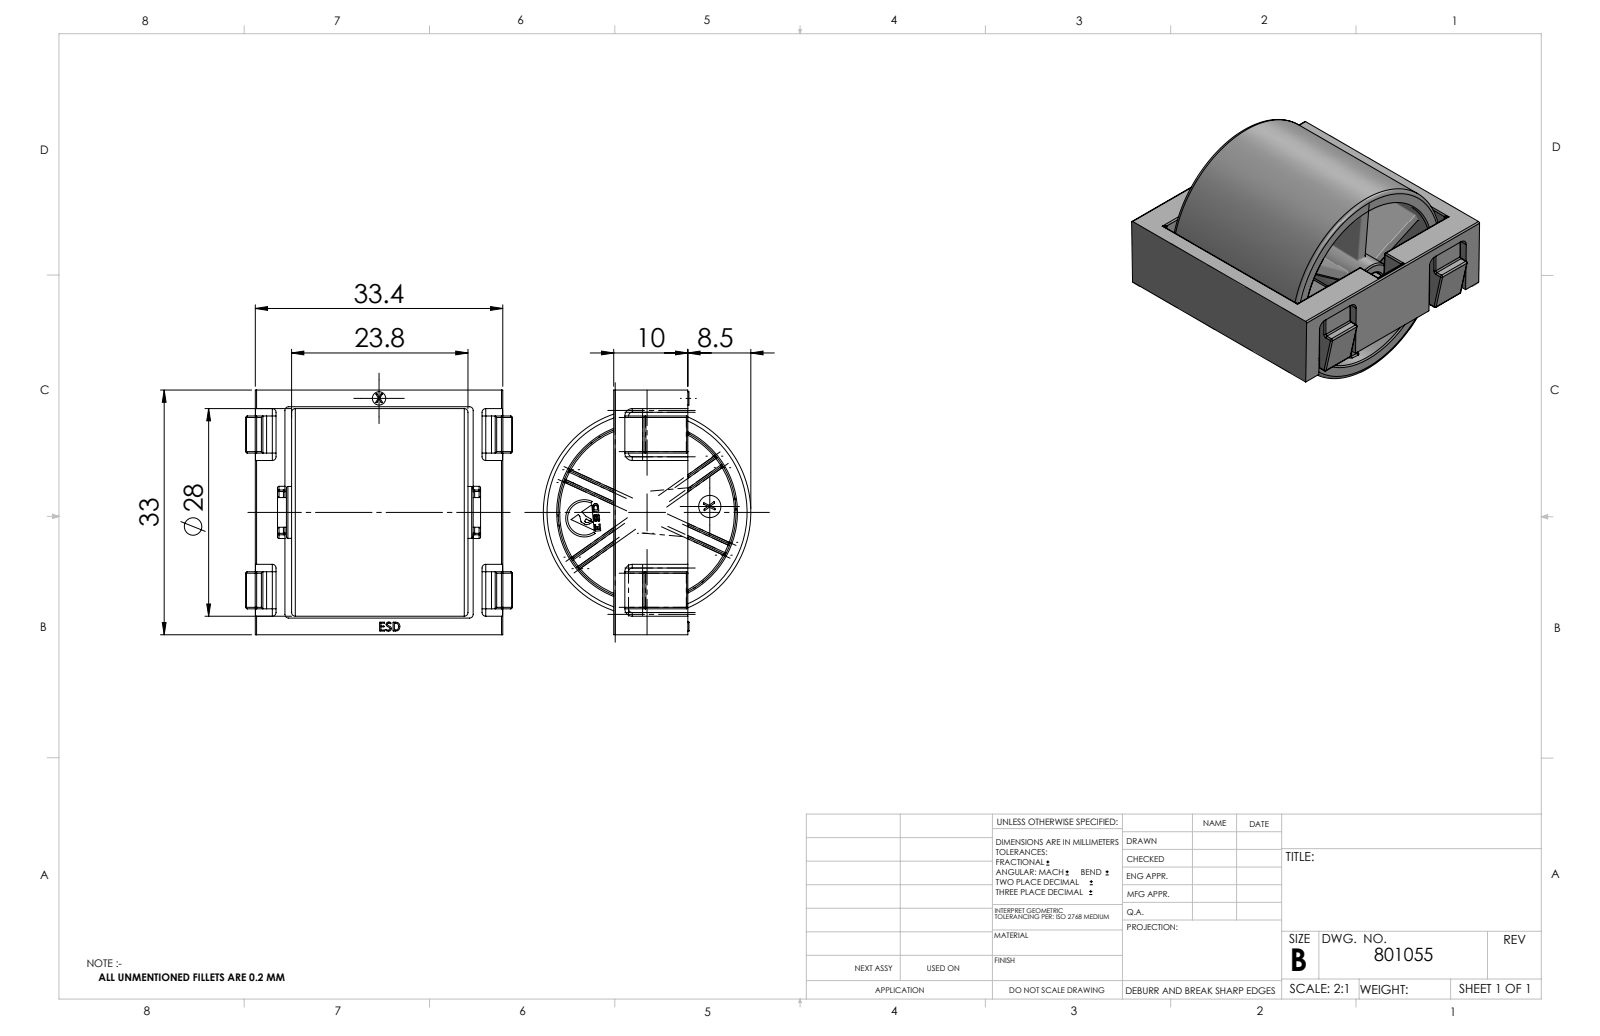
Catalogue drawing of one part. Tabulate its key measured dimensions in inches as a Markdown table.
| quantity | value |
| --- | --- |
| part name | 801055_c_1 |
| STEP written by | SolidWorks 2014 (CONFIG_CONTROL_DESIGN) |
| units | inches |
| bodies | 3 solids, 808 faces (263 planar, 259 cylindrical, 286 other) |
| overall size | 1.413 × 1.299 × 1.102 |
| volume | 0.602 in³ |
| surface area | 18.09 in² |
| round holes (diameter × count) | 0.165 × 1, 0.945 × 1 |
| round bosses / shafts (diameter × count) | 1.102 × 1, 0.276 × 1, 0.157 × 1, 0.118 × 1, 0.071 × 1 |
| partial cylindrical surfaces (radius × count) | 0.008 × 152, 0.02 × 16, 0.039 × 4, 0.081 × 1, 0.089 × 1, 0.099 × 1 |
| main face-to-face distances | 0.059, 0.089, 1.211, 1.299, 0.394, 0.031, 0.48, 0.512, 0.52, 1.122 |
